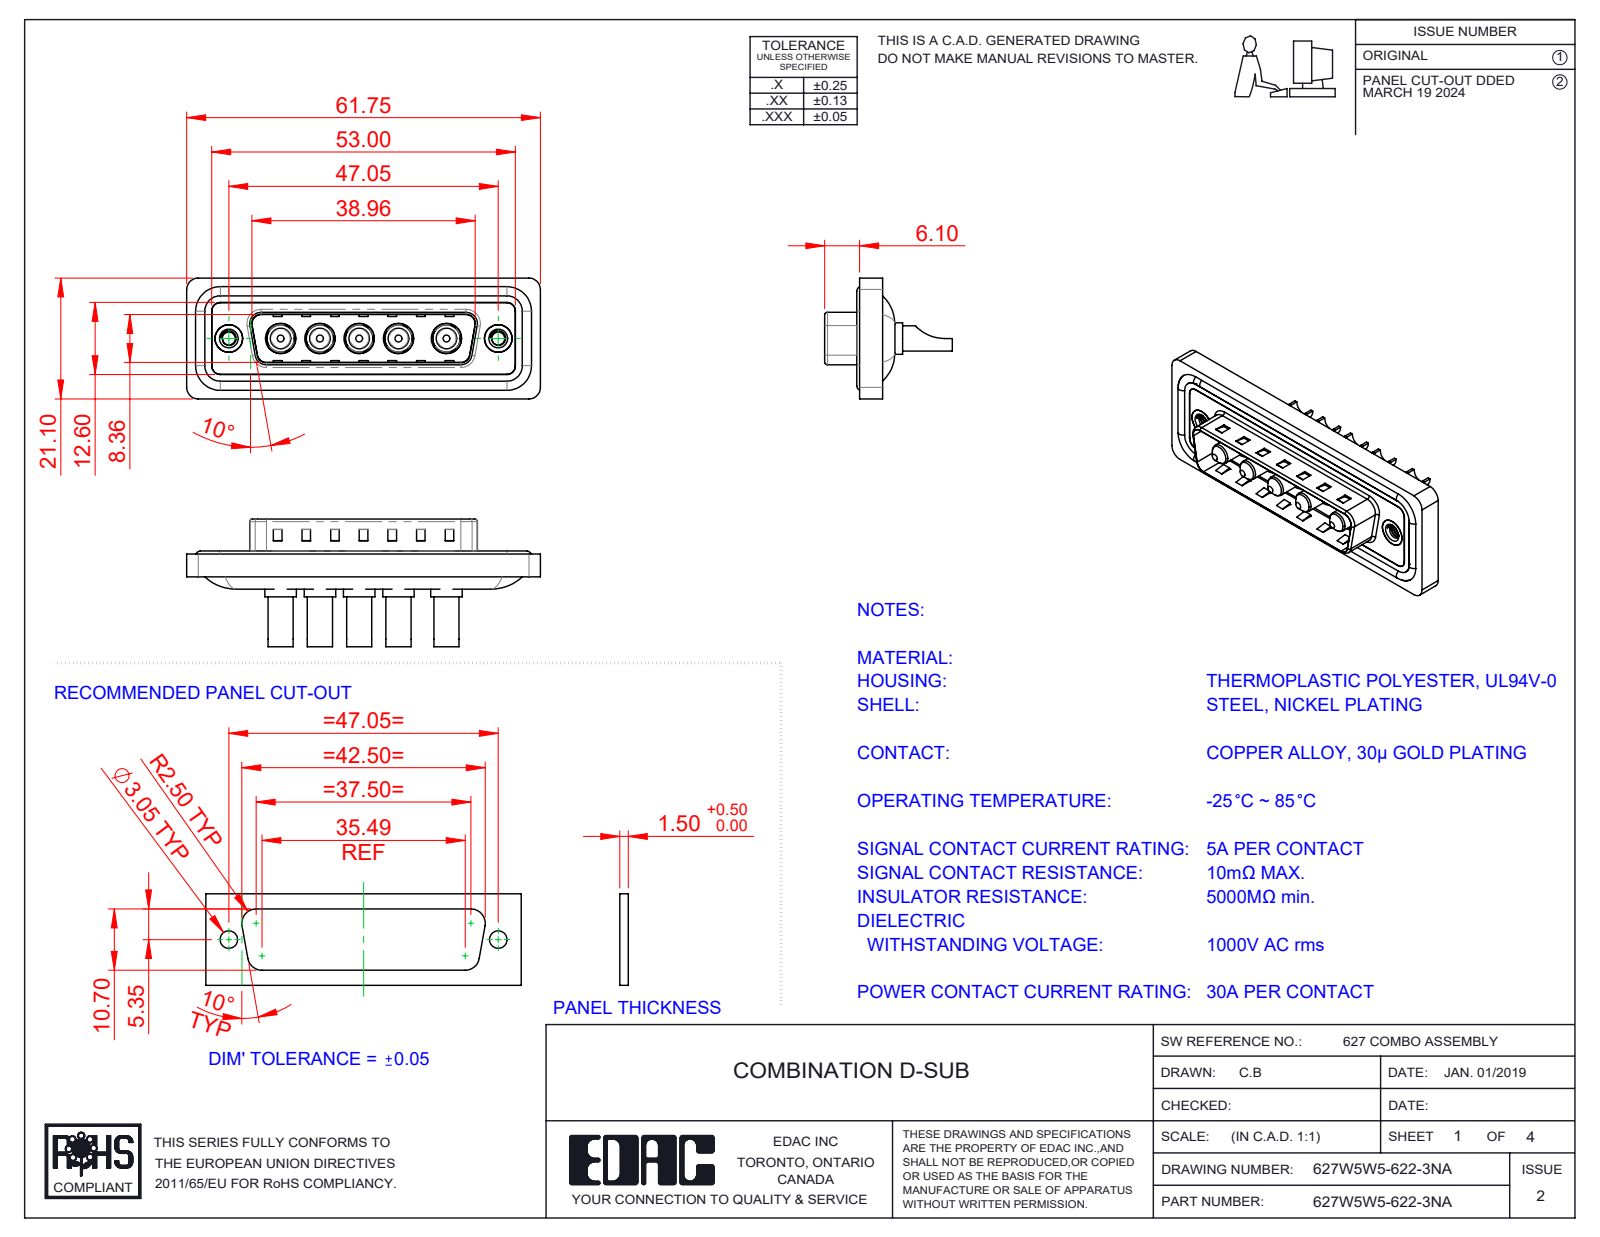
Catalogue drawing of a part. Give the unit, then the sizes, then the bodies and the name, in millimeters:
Units: millimetres
Overall size (bounding box): 61.75 × 22.3 × 21.1
Round holes (diameter × count): ⌀3.5 ×5, ⌀4.85 ×5, ⌀5.3 ×5, ⌀2.26 ×2, ⌀4 ×2, ⌀4.8 ×2, ⌀5 ×2
Round bosses / shafts (diameter × count): ⌀5.5 ×5, ⌀5.2 ×5, ⌀4.75 ×5, ⌀4.4 ×5, ⌀3.75 ×5, ⌀3.6 ×5, ⌀1.6 ×4, ⌀4.9 ×2
Partial cylindrical surfaces — rounded edges, fillets, slot ends (radius × count): R1.5 ×22, R2 ×18, R0.5 ×8, R1.6 ×8, R2.1 ×5, R0.25 ×4, R0.6 ×4, R0.65 ×4
Main face-to-face distances: 0.4, 1.5, 0.5, 1.1, 3.1, 1.6, 2.9, 0.82, 9.58, 5.65
Hole centre spacings: 6.86, 9.04, 13.73, 38.01, 6.87, 8.37, 8.38, 9.05
Volume: 7 595 mm³ · Surface area: 12 331 mm²
Bodies: 17 solids, 706 faces (274 planar, 300 cylindrical, 132 other)
Part name (STEP PRODUCT): 627Combo Shell Rear_25 Contacts; Power Pin_30A SC; 627Combo Waterproof Housing_25 Contacts; 627Combo Shell Front_25 Contacts (+3 more)
STEP written by: SolidWorks 2023 (CONFIG_CONTROL_DESIGN)
